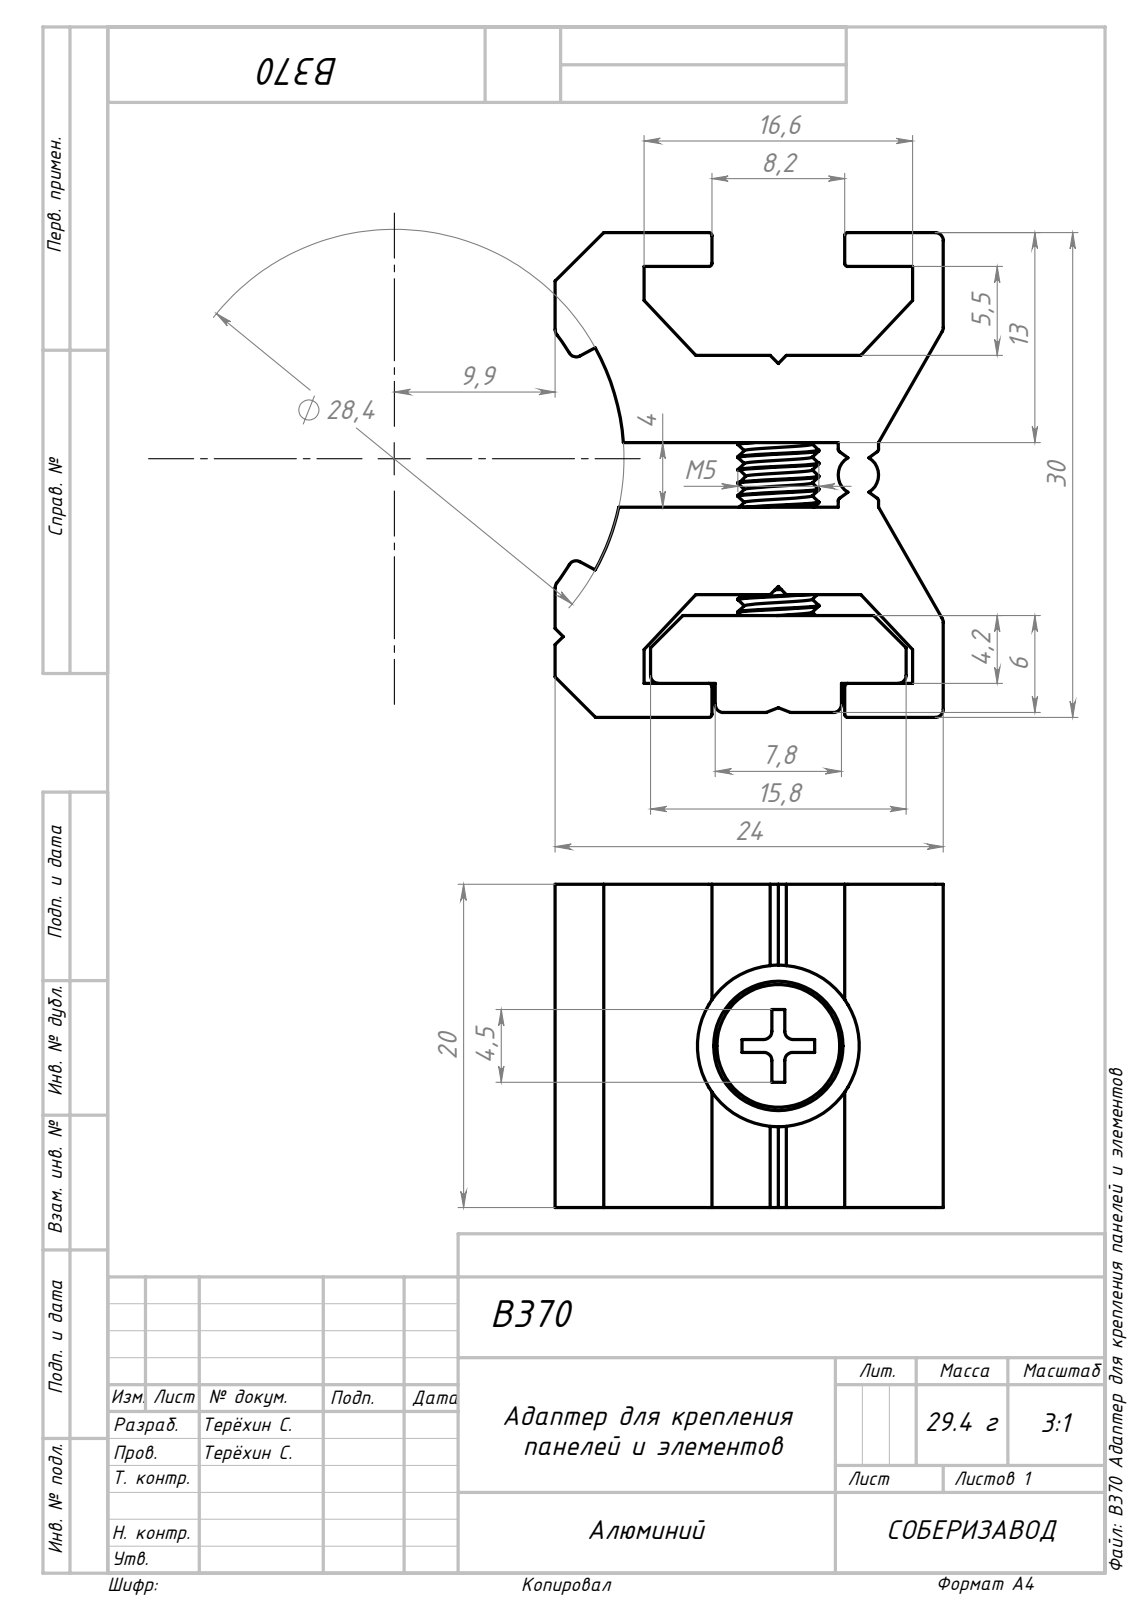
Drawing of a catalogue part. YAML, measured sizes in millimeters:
part_name: "B370 Адаптер для крепления панелей и элементов"
step_written_by: "SolidWorks 2022 (AUTOMOTIVE_DESIGN)"
units: millimeters
bodies: {solids: 3, faces: 252, planar: 93, cylindrical: 114, other: 45}
overall_size: [30, 24, 20]
volume: 8349
surface_area: 6144
round_holes:
  - {diameter: 4.2, count: 1}
  - {diameter: 5.5, count: 1}
  - {diameter: 10, count: 1}
round_bosses_or_shafts:
  - {diameter: 8, count: 1}
  - {diameter: 5, count: 1}
partial_cylinders:
  - {radius: 0.5, count: 16}
  - {radius: 0.2, count: 12}
  - {radius: 1.25, count: 1}
  - {radius: 12.65, count: 1}
  - {radius: 14.2, count: 1}
face_to_face_distances: [13, 17, 2.1, 10.9, 14.9, 20, 27.9, 5.5, 4, 4.2]
